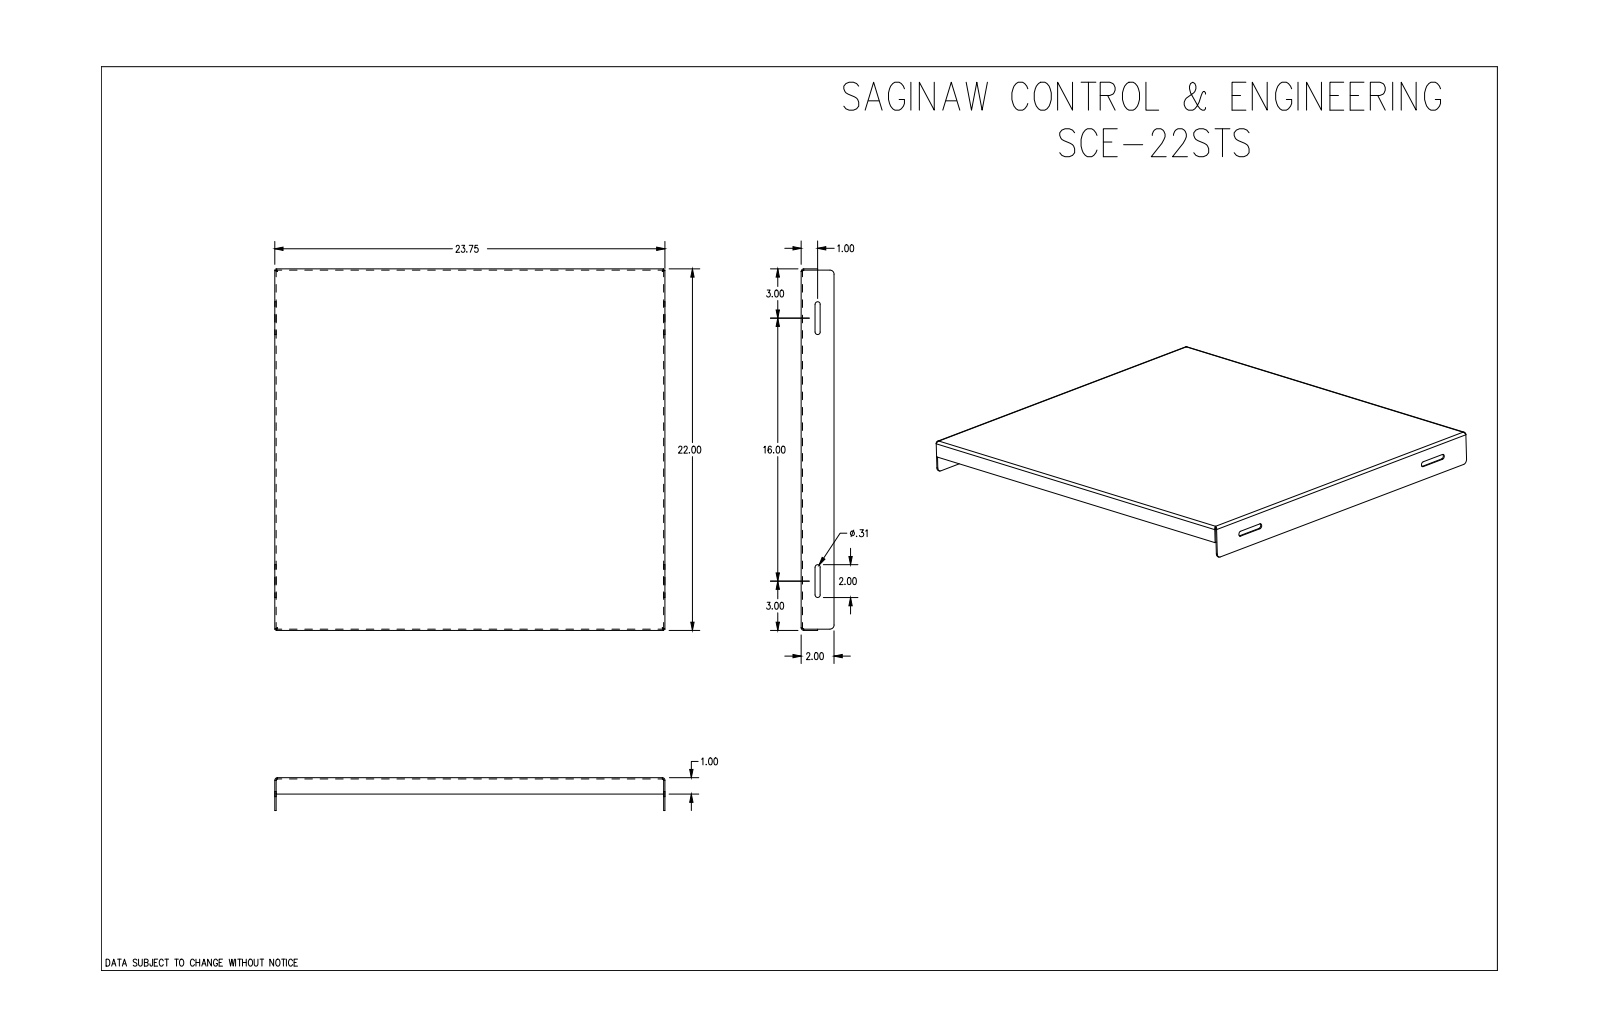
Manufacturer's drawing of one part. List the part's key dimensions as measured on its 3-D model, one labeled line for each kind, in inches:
Part name (STEP PRODUCT): SCE-22STS
STEP written by: SolidWorks 2019 (CONFIG_CONTROL_DESIGN)
Units: inches
Bodies: 1 solid, 62 faces (30 planar, 24 cylindrical, 8 other)
Overall size (bounding box): 23.75 × 22 × 2
Volume: 50.14 in³ · Surface area: 1 295 in²
Partial cylindrical surfaces — rounded edges, fillets, slot ends (radius × count): R0.078 ×4, R0.156 ×4, R0.156 ×4, R0.02 ×2, R0.25 ×2
Main face-to-face distances: 0.078, 23.672, 21.922, 23.594, 23.75, 21.844, 22, 1, 0.922, 1.922
